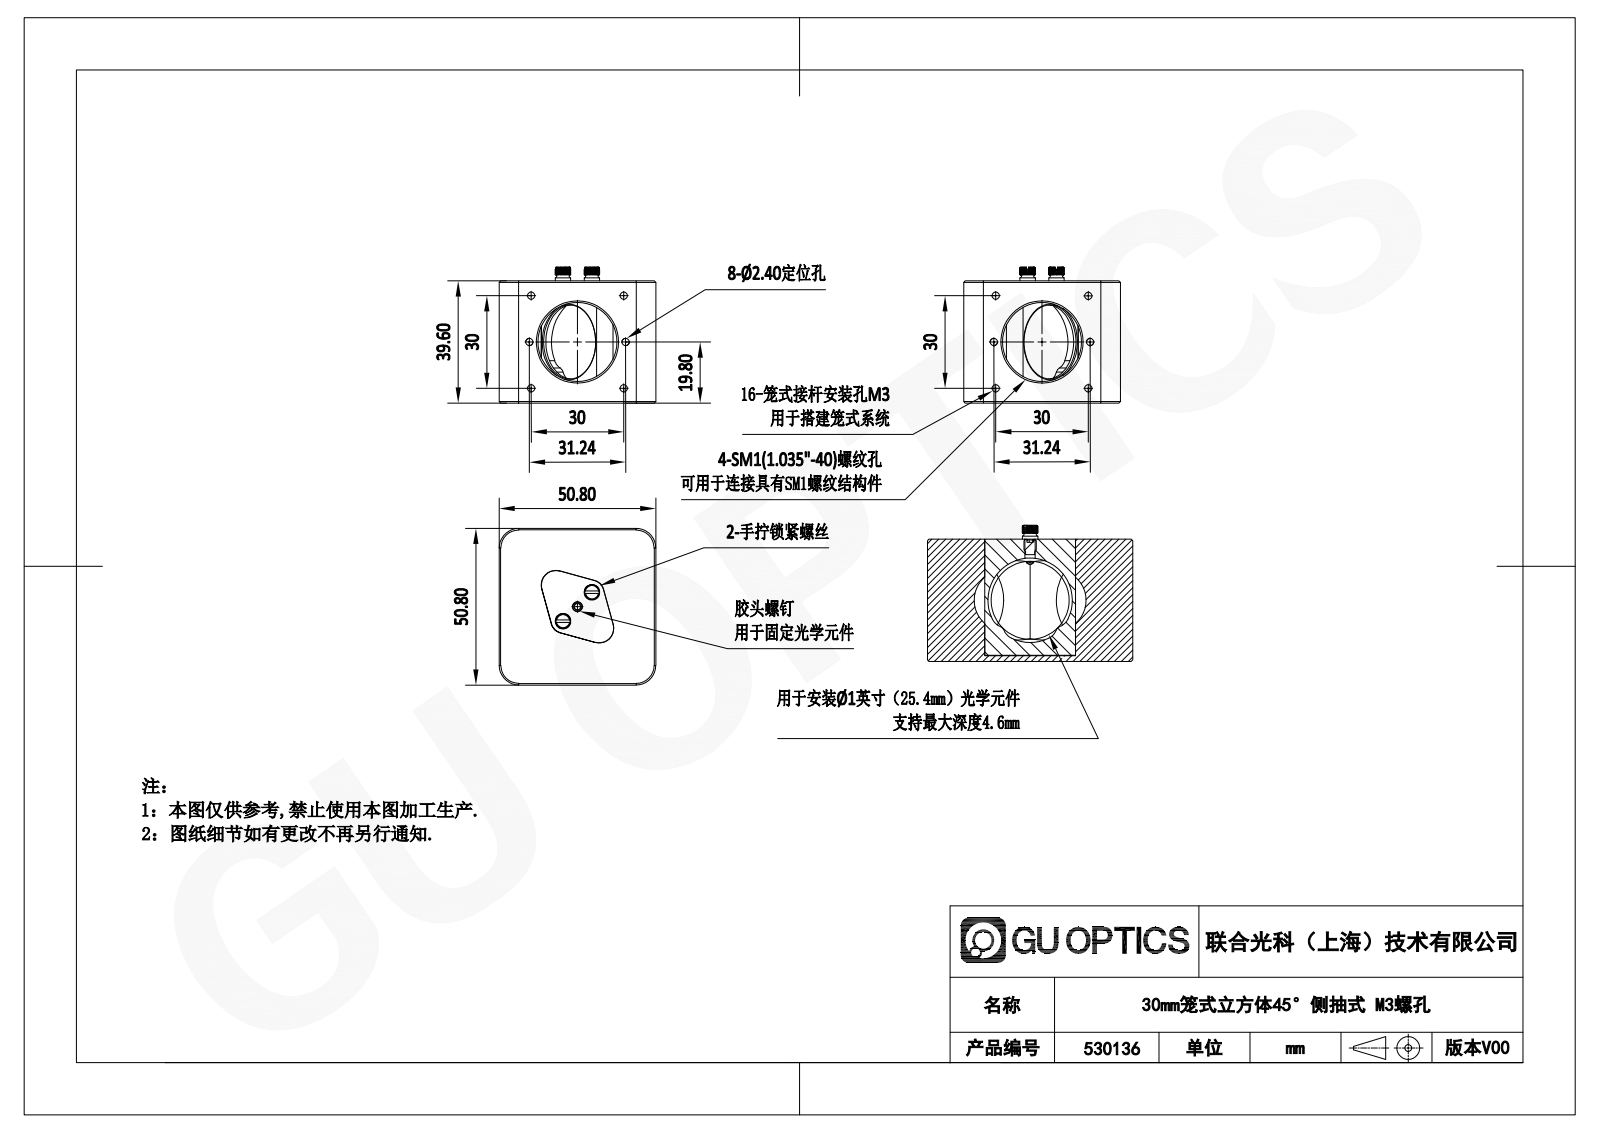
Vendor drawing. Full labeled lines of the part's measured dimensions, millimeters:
Part name (STEP PRODUCT): 530136
STEP written by: SolidWorks 2020 (CONFIG_CONTROL_DESIGN)
Units: millimetres
Bodies: 5 solids, 379 faces (199 planar, 128 cylindrical, 52 other)
Overall size (bounding box): 50.8 × 50.8 × 44.34
Volume: 58 889 mm³ · Surface area: 21 188 mm²
Round holes (diameter × count): ⌀2.5 ×10, ⌀2.44 ×4, ⌀25.69 ×2, ⌀3.3 ×1, ⌀24 ×1
Round bosses / shafts (diameter × count): ⌀3 ×3, ⌀5 ×2, ⌀2 ×2, ⌀4 ×1
Partial cylindrical surfaces — rounded edges, fillets, slot ends (radius × count): R4 ×4, R5 ×4, R6.35 ×4, R2.5 ×2, R4.7 ×2, R13.7 ×1
Main face-to-face distances: 39.6, 50.8, 39.84, 3, 2, 6, 0.8, 34.8, 8.6, 37.6
Hole centre spacings: 15.01, 21.21, 30, 34.1, 15.62, 42.43, 6.62, 31.24
